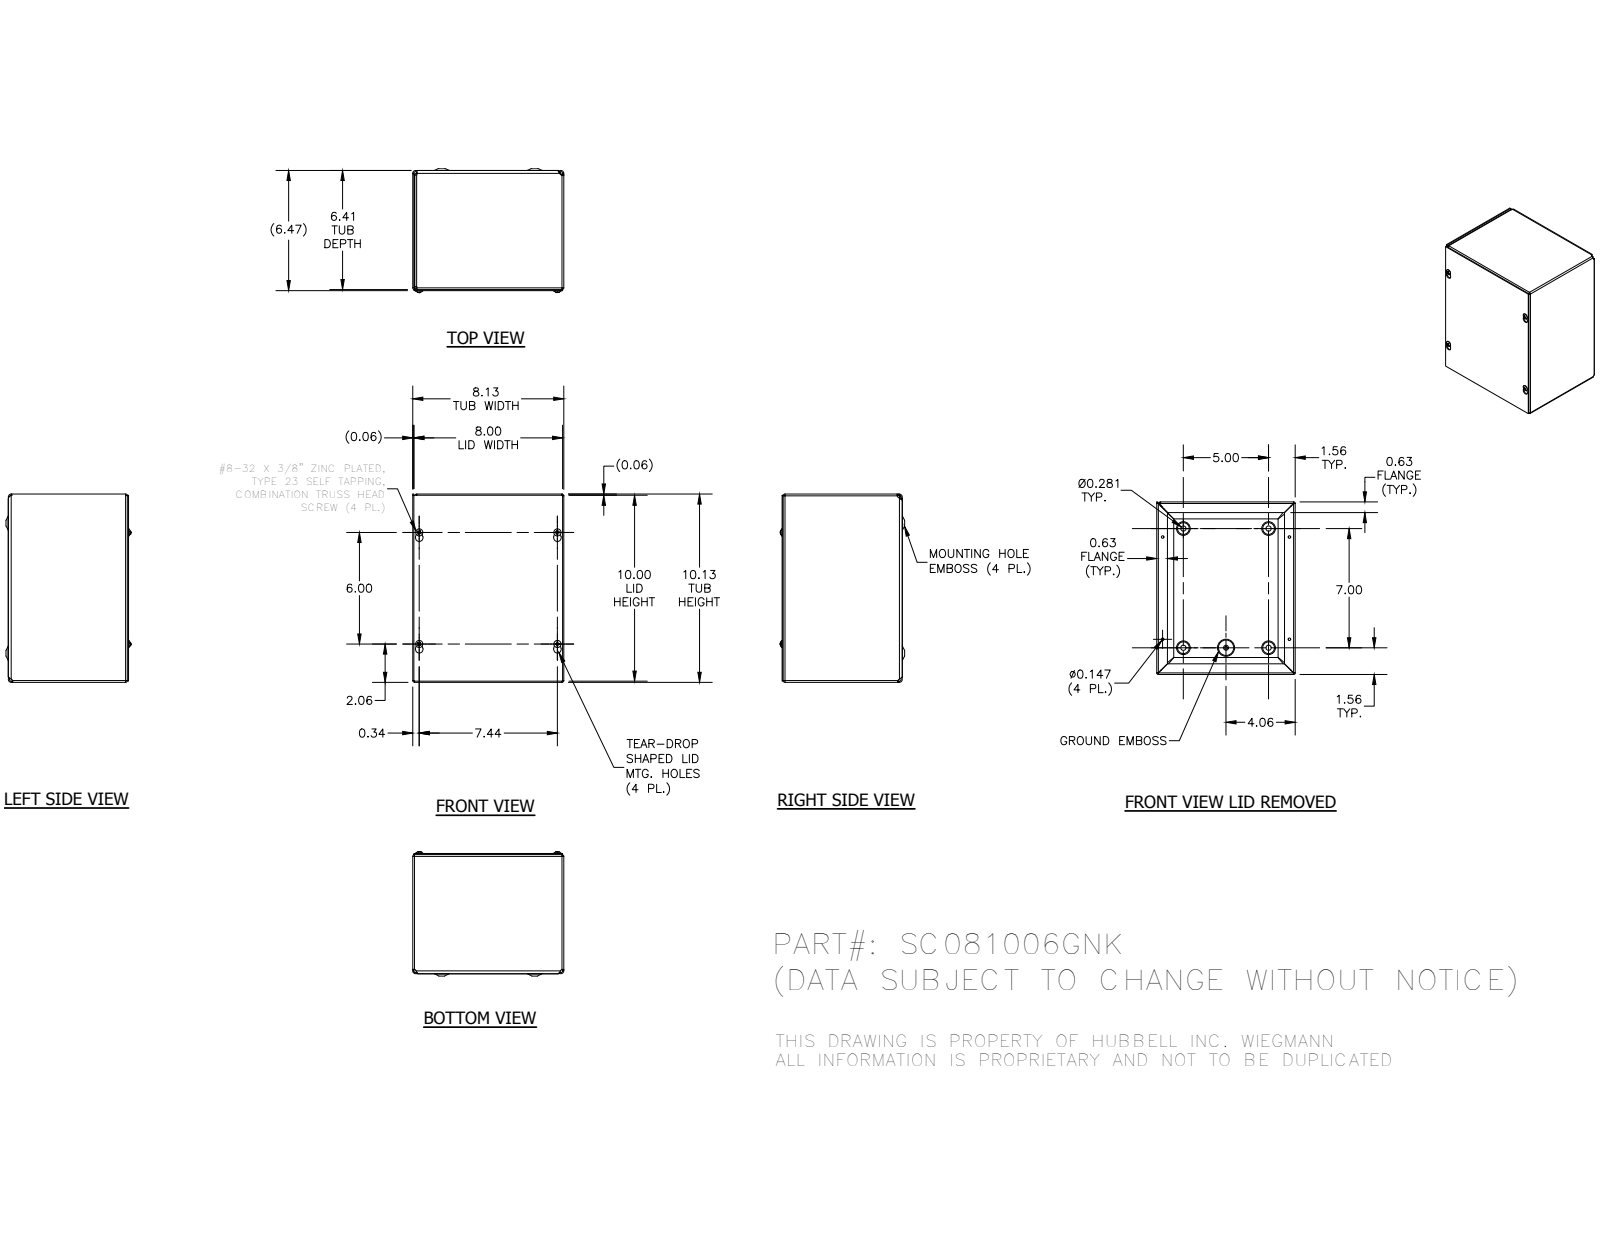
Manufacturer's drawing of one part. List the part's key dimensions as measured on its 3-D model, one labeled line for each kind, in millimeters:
Part name (STEP PRODUCT): SC0810GNKBKP; SC081006GNKWRA; SC0810GNKLID; 34056 (+1 more)
STEP written by: Autodesk Inventor 2014 (AUTOMOTIVE_DESIGN)
Units: millimetres
Bodies: 7 solids, 358 faces (133 planar, 73 cylindrical, 152 other)
Overall size (bounding box): 257.18 × 206.38 × 170
Volume: 442 120 mm³ · Surface area: 568 269 mm²
Round holes (diameter × count): ⌀3.73 ×4, ⌀7.62 ×4, ⌀4.19 ×1
Round bosses / shafts (diameter × count): ⌀9.75 ×4, ⌀4.17 ×4, ⌀5.8 ×1
Partial cylindrical surfaces — rounded edges, fillets, slot ends (radius × count): R0.79 ×8, R2.37 ×8, R1.4 ×4, R1.57 ×4, R2.38 ×4, R2.97 ×4, R3.15 ×4, R3.17 ×4
Main face-to-face distances: 1.57, 1.58, 161.12, 162.69, 1.59, 162.71, 164.28, 206.38, 204.81, 204.8
Hole centre spacings: 33.46, 63.5, 127, 152.4, 158.46, 158.47, 167.96, 168
